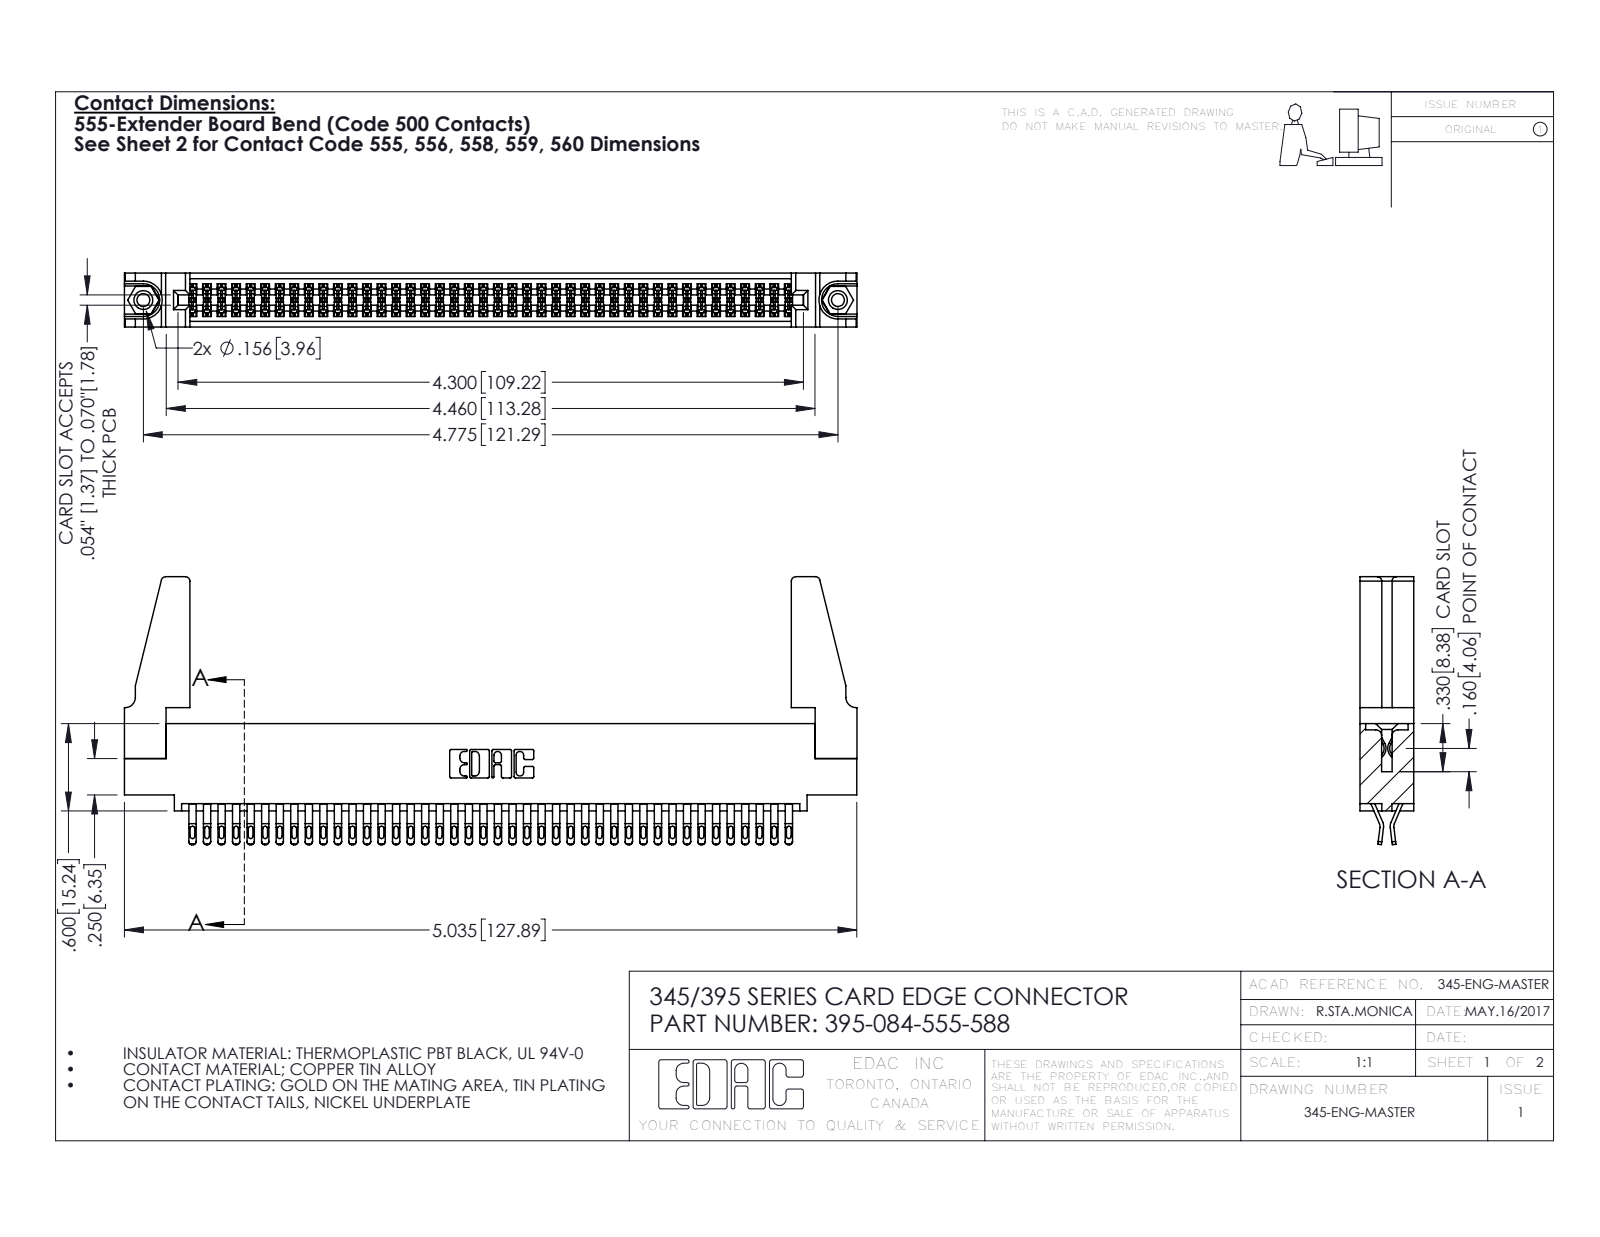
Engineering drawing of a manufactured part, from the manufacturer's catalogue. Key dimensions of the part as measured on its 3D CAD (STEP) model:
Part name (STEP PRODUCT): 345-220-078_345-220-088; 345-292-001_555 Tail; 345 Part_0.110 Offset - 0.156 Dia-TH; 395-084-555-588 (+1 more)
STEP written by: SolidWorks 2016 (CONFIG_CONTROL_DESIGN)
Units: inches
Bodies: 89 solids, 4958 faces (2760 planar, 2182 cylindrical, 16 other)
Overall size (bounding box): 5.036 × 1.842 × 0.37
Volume: 0.967 in³ · Surface area: 35.16 in²
Round holes (diameter × count): ⌀0.089 ×2, ⌀0.125 ×2, ⌀0.156 ×2, ⌀0.064 ×1
Round bosses / shafts (diameter × count): ⌀0.155 ×2
Partial cylindrical surfaces — rounded edges, fillets, slot ends (radius × count): R0.016 ×210, R0.02 ×168, R0.006 ×126, R0.01 ×22, R0.03 ×8, R0.007 ×6, R0.031 ×6, R0.026 ×3
Main face-to-face distances: 0.072, 0.298, 0.37, 0.025, 0.2, 0.098, 0.272, 0.225, 0.175, 0.149
Hole centre spacings: 0.27, 4.539, 4.775
